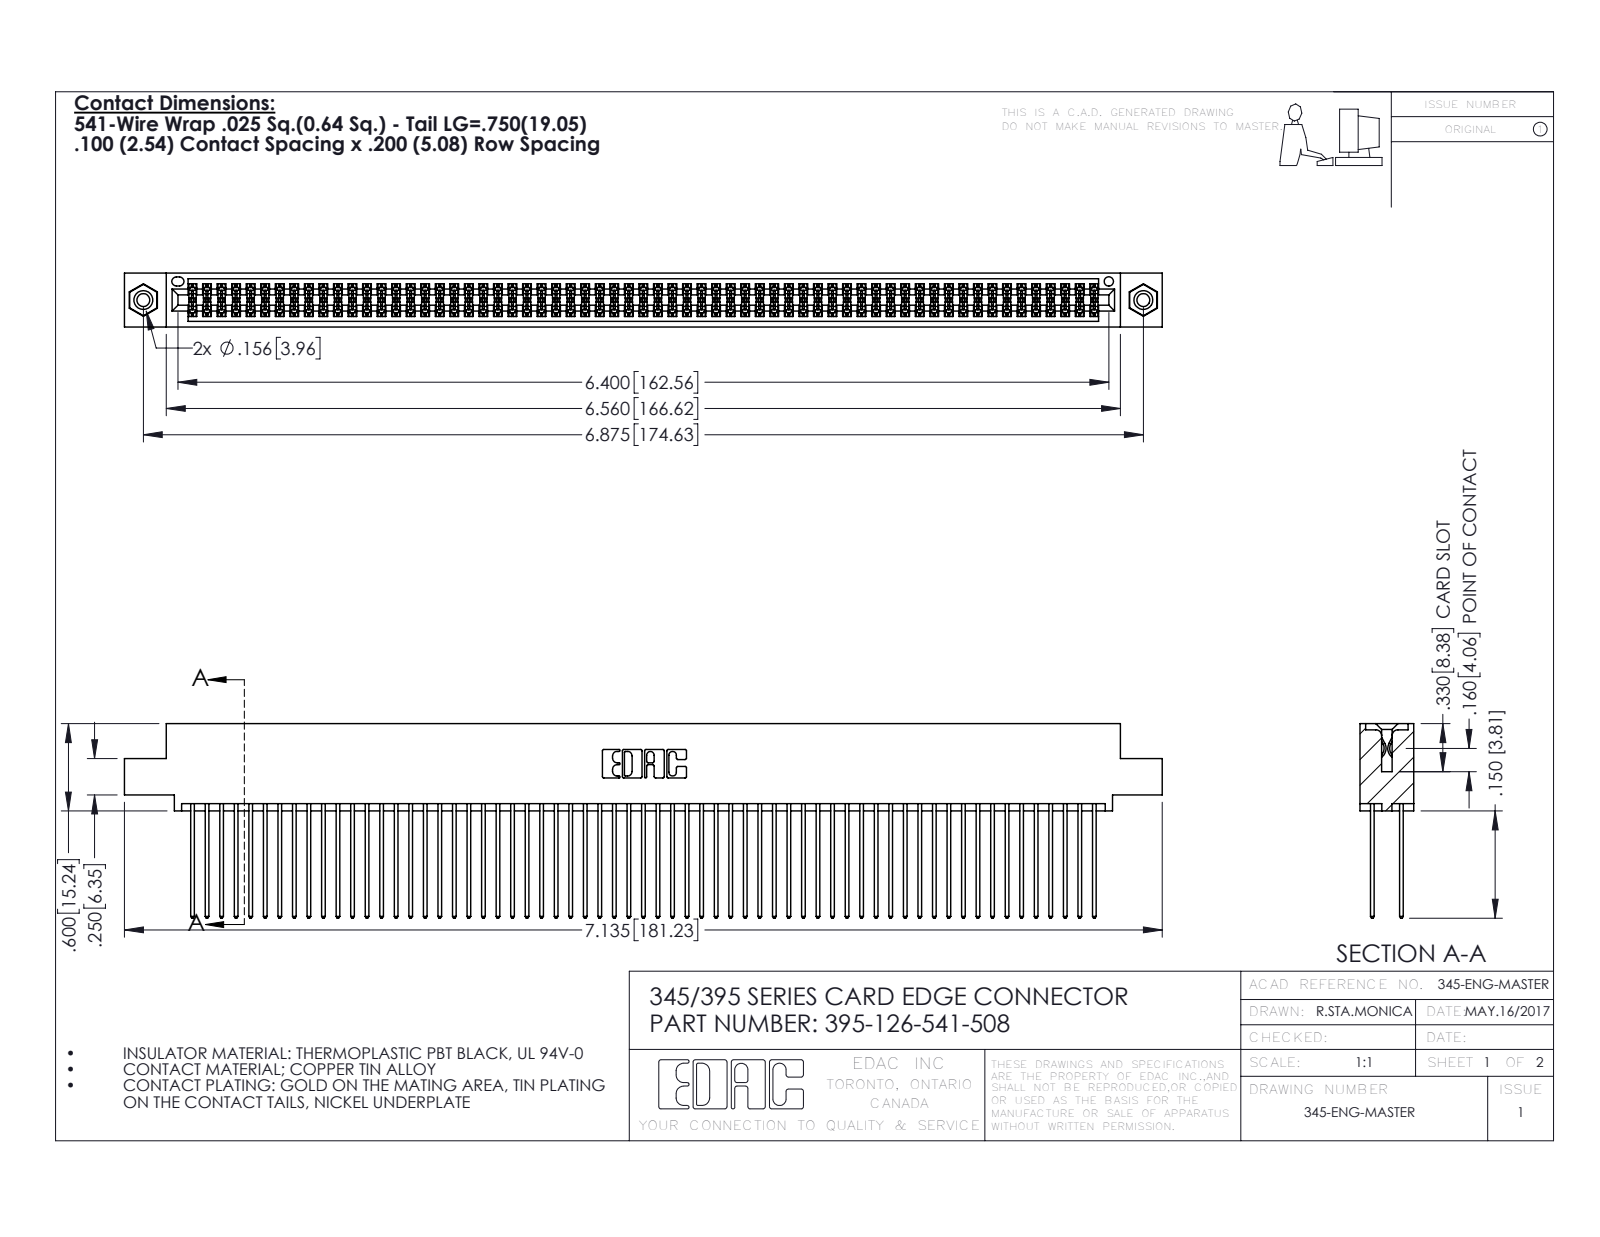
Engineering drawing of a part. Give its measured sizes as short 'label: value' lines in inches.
name: 395-126-541-508; 345 Part_0.110 Offset - 0.156 Dia-TI; 345-250-001_345-250-003-102; 345-292-001_345-293-141
written by: SolidWorks 2016 (CONFIG_CONTROL_DESIGN)
unit: in
bodies: 129 solids, 6490 faces (4274 planar, 2200 cylindrical, 16 other)
size: 7.135 × 1.337 × 0.37
volume: 1.125 in³; area: 48.32 in²
holes: 2× ⌀0.089, 2× ⌀0.125, 2× ⌀0.156, 1× ⌀0.064
bosses: 2× ⌀0.155
rounds: 189× R0.006, 126× R0.01, 22× R0.01, 6× R0.007, 6× R0.031, 3× R0.026, 2× R0.014, 2× R0.019
face distances: 0.072, 0.298, 0.2, 0.098, 0.272, 0.025, 0.225, 0.37, 0.175, 0.149
hole spacings: 0.27, 6.639, 6.875
